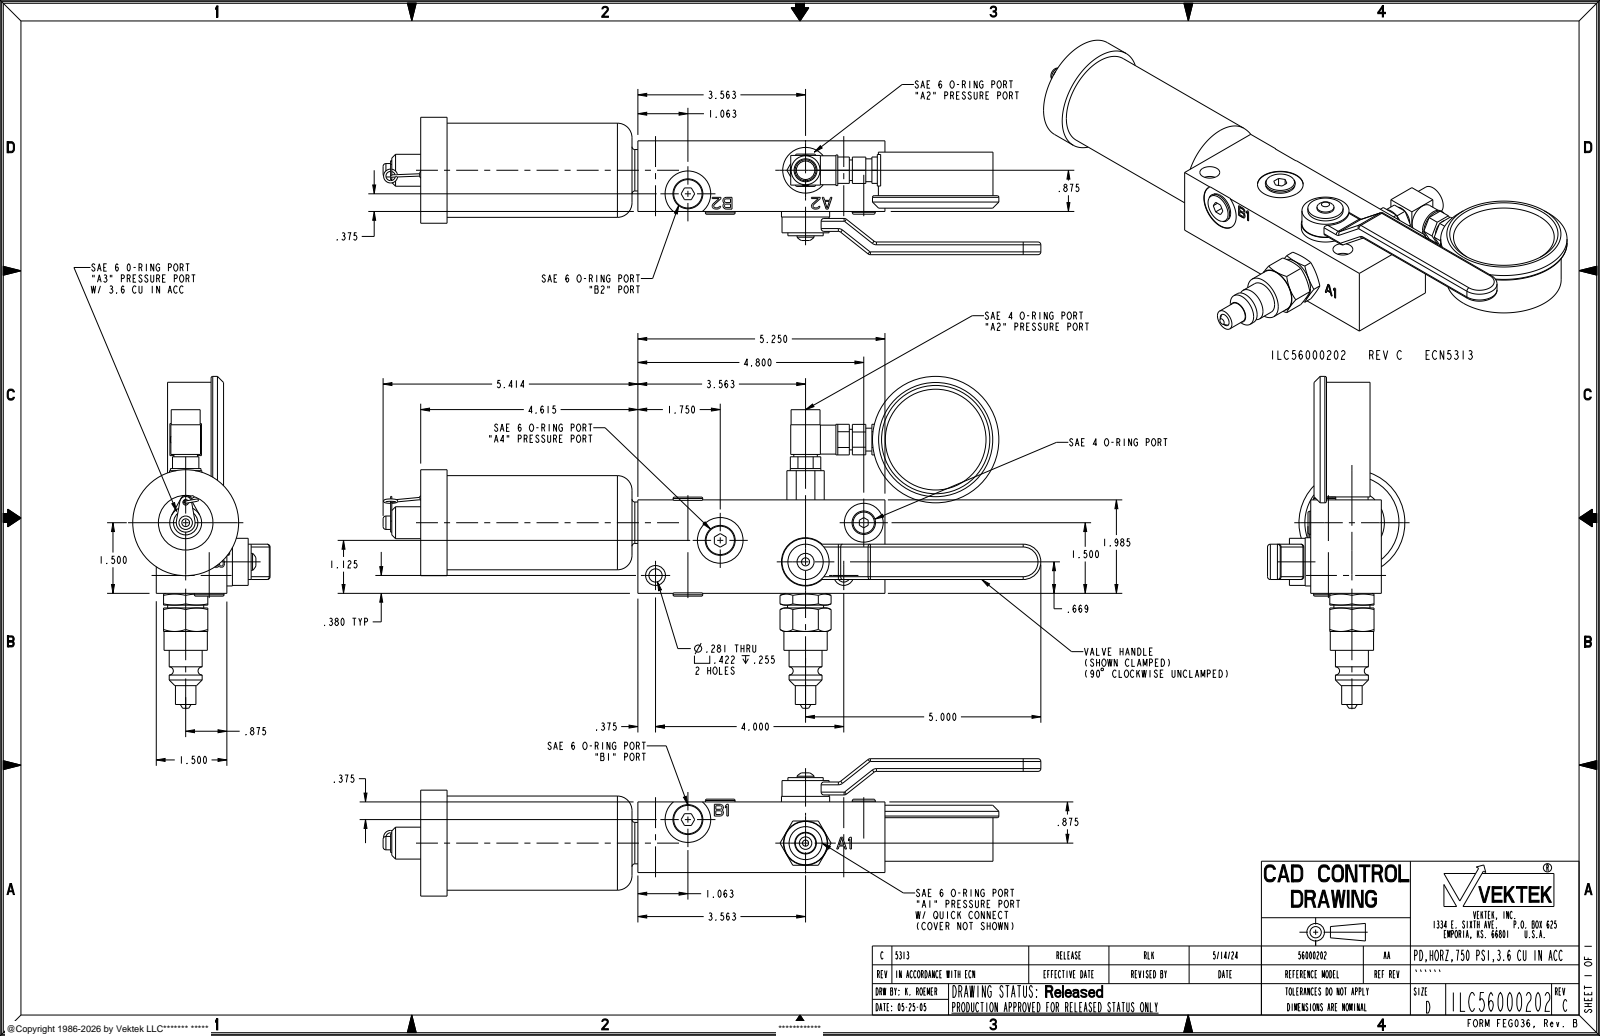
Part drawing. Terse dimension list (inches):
name: ILC56000202
written by: CREO PARAMETRIC BY PTC INC, 2021164 (AUTOMOTIVE_DESIGN)
unit: in
bodies: 5 solids, 685 faces (436 planar, 141 cylindrical, 108 other)
size: 13.977 × 7.048 × 2.918
volume: 38.15 in³; area: 150.4 in²
holes: 4× ⌀0.515, 3× ⌀0.97, 2× ⌀0.118, 2× ⌀0.281, 2× ⌀0.392, 2× ⌀0.422, 1× ⌀0.12, 1× ⌀0.265, 1× ⌀0.442, 1× ⌀0.498, 1× ⌀0.825, 1× ⌀1.16
bosses: 4× ⌀0.563, 3× ⌀0.437, 2× ⌀0.65, 2× ⌀0.615, 2× ⌀0.51, 1× ⌀2.685, 1× ⌀2.435, 1× ⌀2.25
rounds: 12× R0.06, 4× R0.08, 1× R0.108, 1× R0.125, 1× R0.2, 1× R0.375, 1× R0.485
face distances: 1.5, 1.985, 0.24, 1.26, 1.35, 1.11, 0.15, 9.865, 4.615, 5.25
hole spacings: 0.039, 0.433, 0.472, 1.198, 1.564, 2.55, 2.729, 3.072
